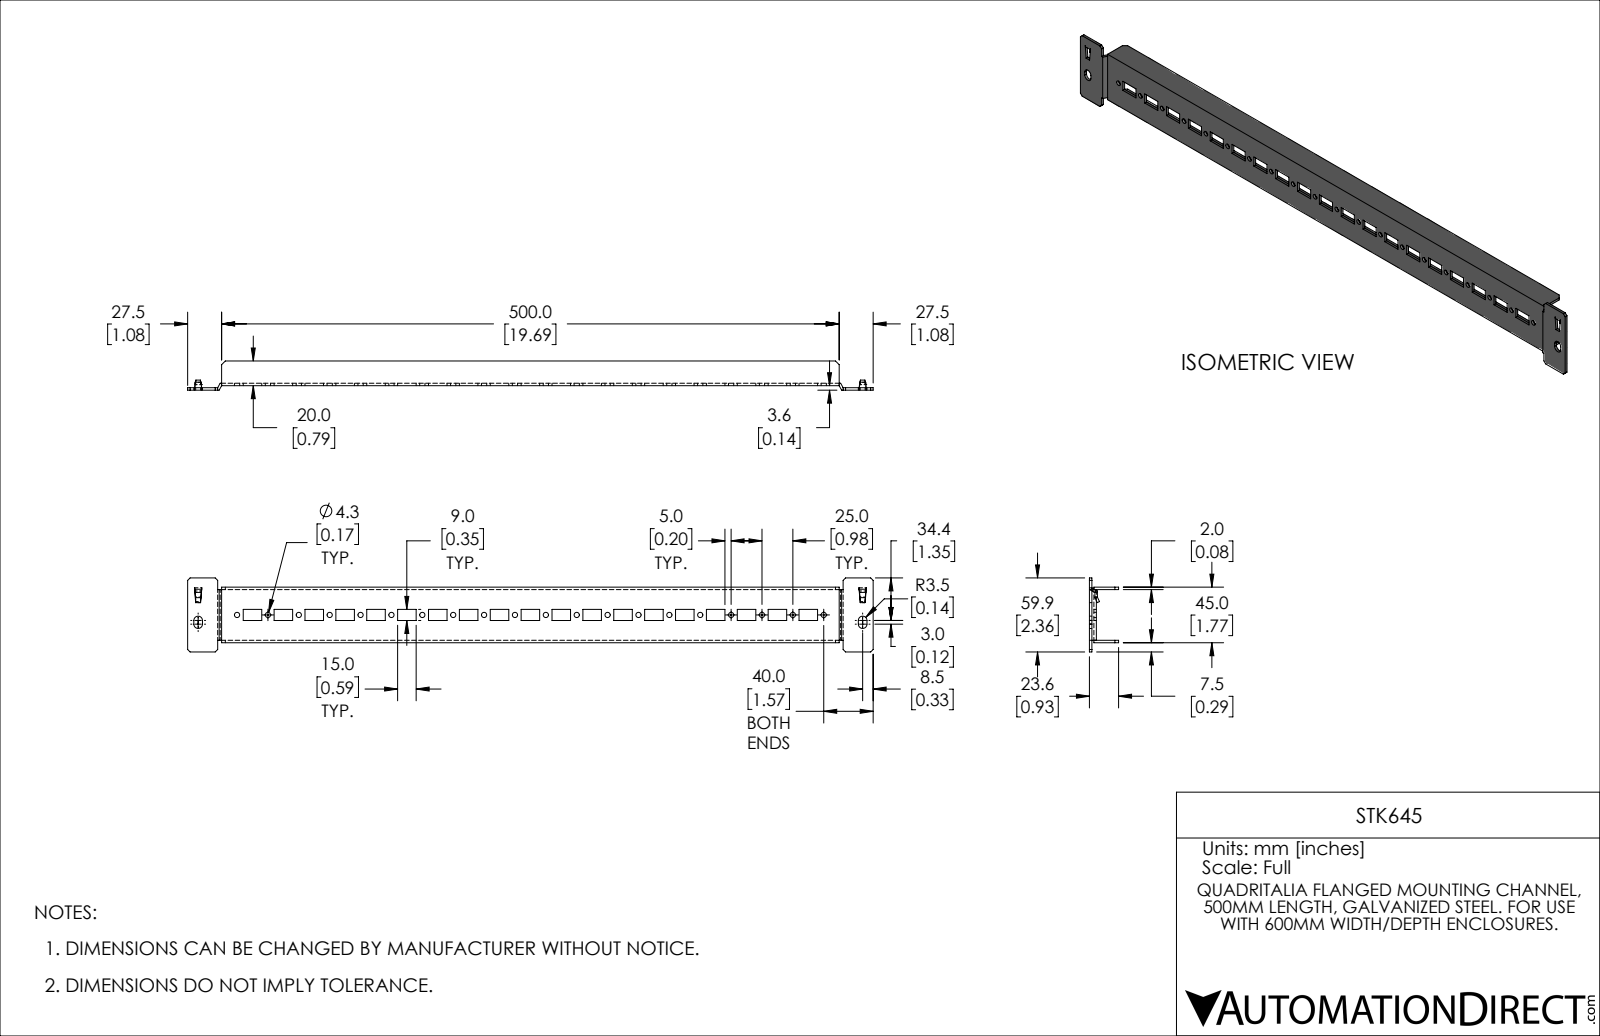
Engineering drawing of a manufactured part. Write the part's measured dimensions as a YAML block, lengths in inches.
part_name: "STK645"
step_written_by: "SolidWorks 2021 (CONFIG_CONTROL_DESIGN)"
units: inches
bodies: {solids: 1, faces: 206, planar: 170, cylindrical: 24, other: 12}
overall_size: [21.85, 2.359, 0.93]
volume: 4.987
surface_area: 135
round_holes:
  - {diameter: 0.167, count: 20}
partial_cylinders:
  - {radius: 0.138, count: 4}
face_to_face_distances: [0.079, 1.693, 1.772, 1.614, 0.143, 0.709, 0.221, 0.064, 0.787, 0.93]
hole_center_spacings: [0.984, 1.969, 2.953, 3.937, 4.921, 5.906, 6.89, 7.874]
